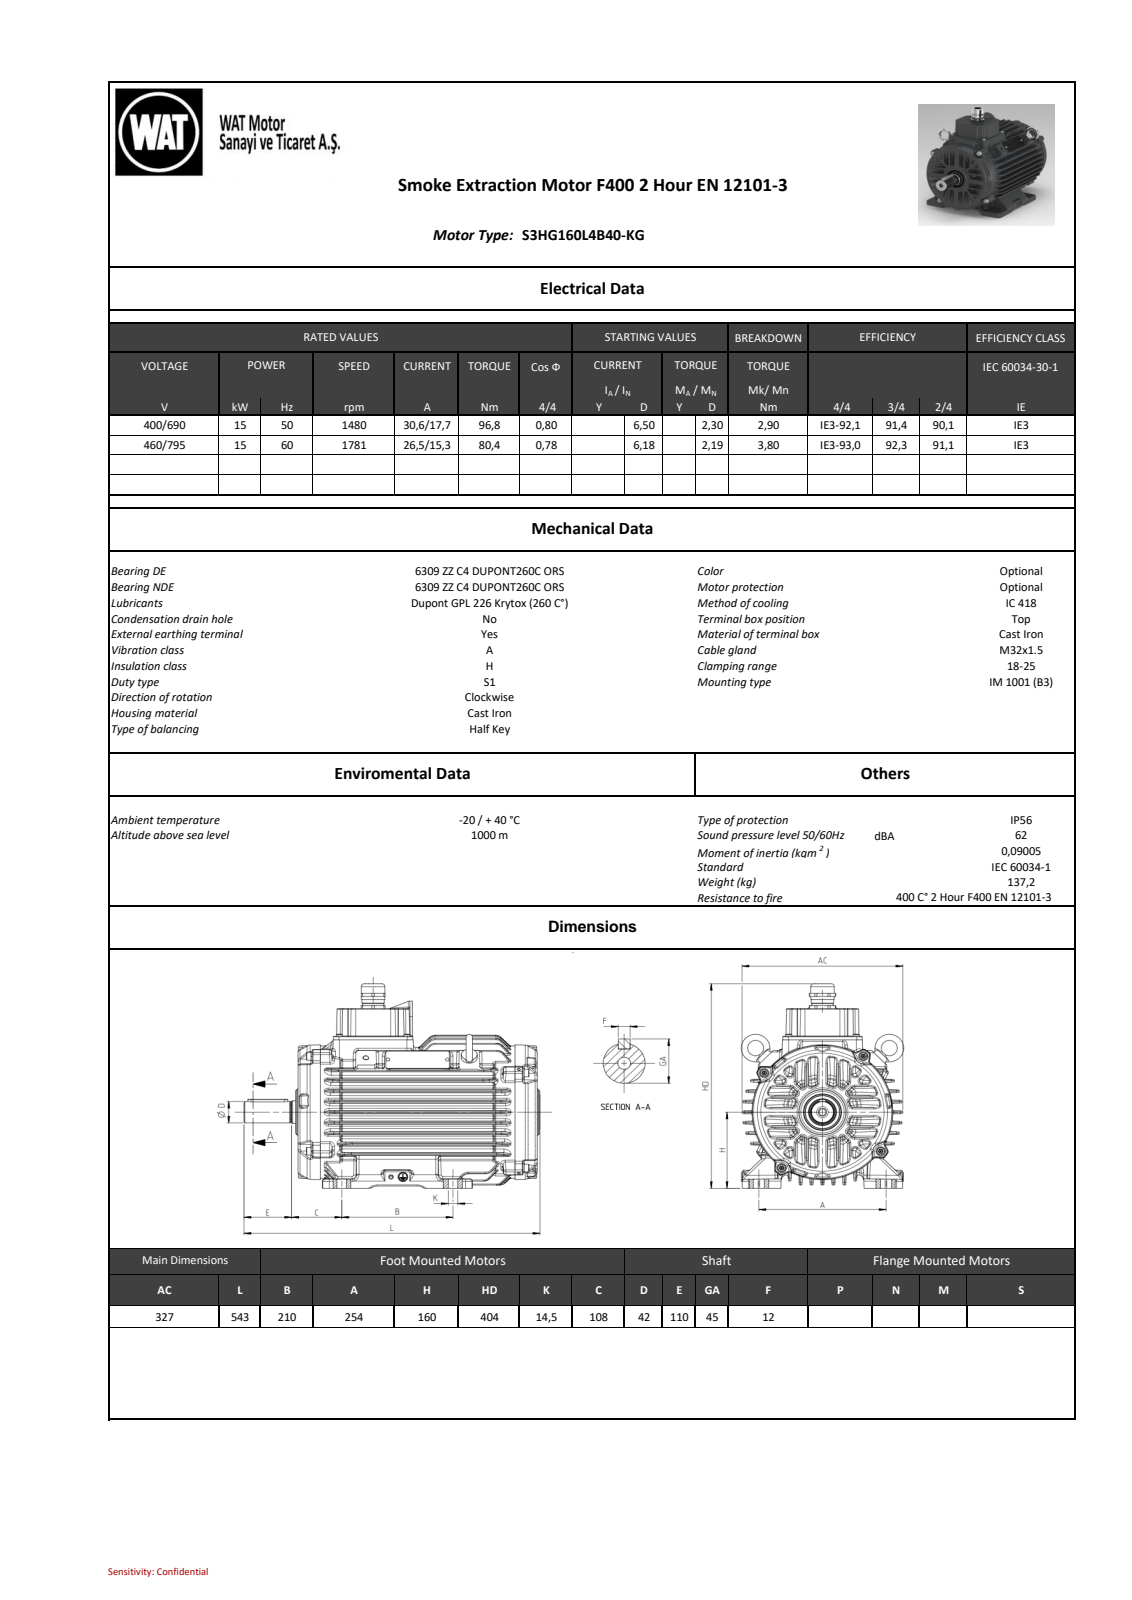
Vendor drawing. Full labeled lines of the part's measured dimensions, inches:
Part name (STEP PRODUCT): 26032C0836B7xjf1
STEP written by: SIEMENS PLM Software NX 11.0 (AUTOMOTIVE_DESIGN)
Units: inches
Bodies: 0 solids, 6176 faces (904 planar, 1512 cylindrical, 3760 other)
Overall size (bounding box): 21.378 × 15.925 × 12.889
Round holes (diameter × count): ⌀0.354 ×7, ⌀0.165 ×4, ⌀0.098 ×2, ⌀0.429 ×2, ⌀0.205 ×1, ⌀0.669 ×1, ⌀0.984 ×1, ⌀2.126 ×1, ⌀2.704 ×1
Round bosses / shafts (diameter × count): ⌀0.787 ×4, ⌀0.63 ×4, ⌀0.619 ×4, ⌀0.394 ×4, ⌀0.713 ×3, ⌀1.181 ×2, ⌀11.102 ×1, ⌀1.772 ×1
Partial cylindrical surfaces — rounded edges, fillets, slot ends (radius × count): R0.197 ×214, R0.118 ×211, R0.157 ×156, R0.059 ×120, R0.079 ×84, R0.071 ×58, R0.138 ×44, R0.016 ×35
Main face-to-face distances: 5.411, 0.597, 0.6, 1.198, 4.811, 1.8, 4.208, 1.203, 0.603, 0.059
Hole centre spacings: 5.669, 8.018, 1.969, 6.504, 9.288, 11.167, 11.339, 1.24
